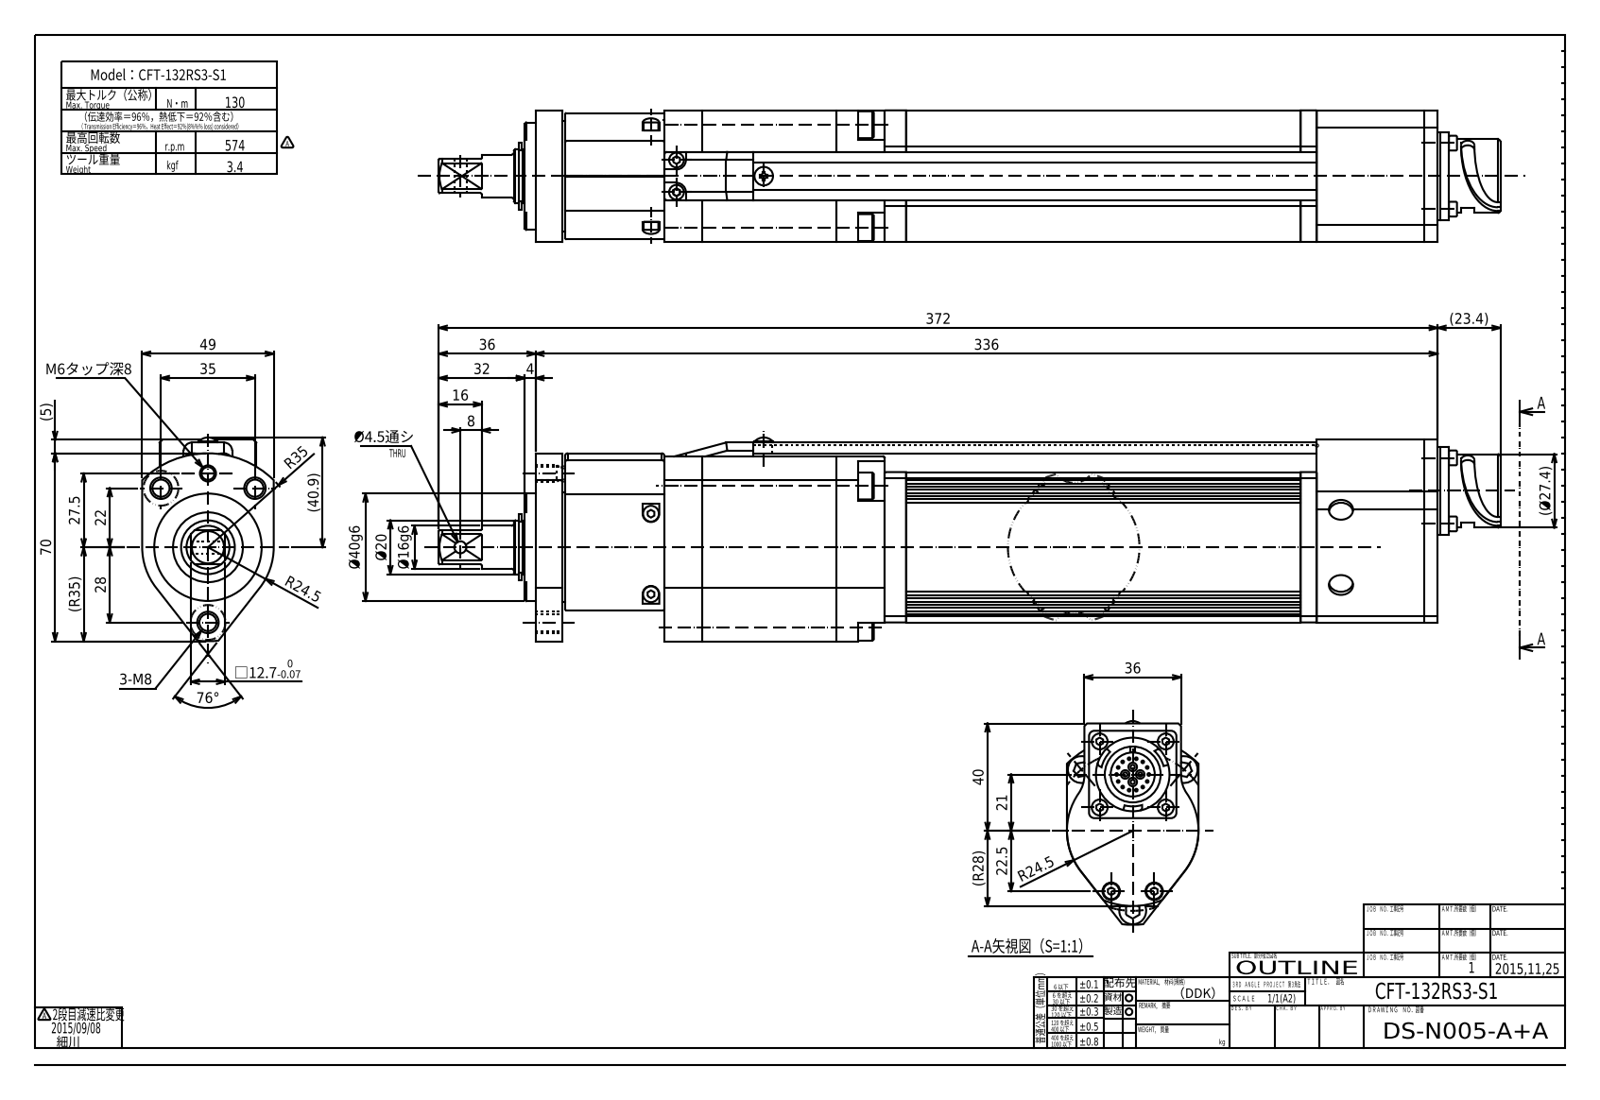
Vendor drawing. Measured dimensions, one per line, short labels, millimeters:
name: CFT-132RS3-S
written by: SolidWorks 2013 (CONFIG_CONTROL_DESIGN)
unit: mm
bodies: 18 solids, 315 faces (129 planar, 134 cylindrical, 52 other)
size: 394.4 × 77.2 × 49
volume: 788 609 mm³; area: 139 365 mm²
holes: 3× ⌀6.8, 1× ⌀4.5, 1× ⌀5, 1× ⌀20.8
bosses: 4× ⌀5.5, 3× ⌀10, 3× ⌀8.5, 1× ⌀47, 1× ⌀41, 1× ⌀40, 1× ⌀27.4, 1× ⌀20
rounds: 7× R0.5, 6× R2, 4× R1, 4× R3, 2× R9, 2× R12, 1× R24.5, 1× R28
face distances: 50, 224, 1, 14, 27, 5, 10, 219, 269, 39
hole spacings: 17.53, 18.34, 52.97, 6.5, 35, 49, 55.5
